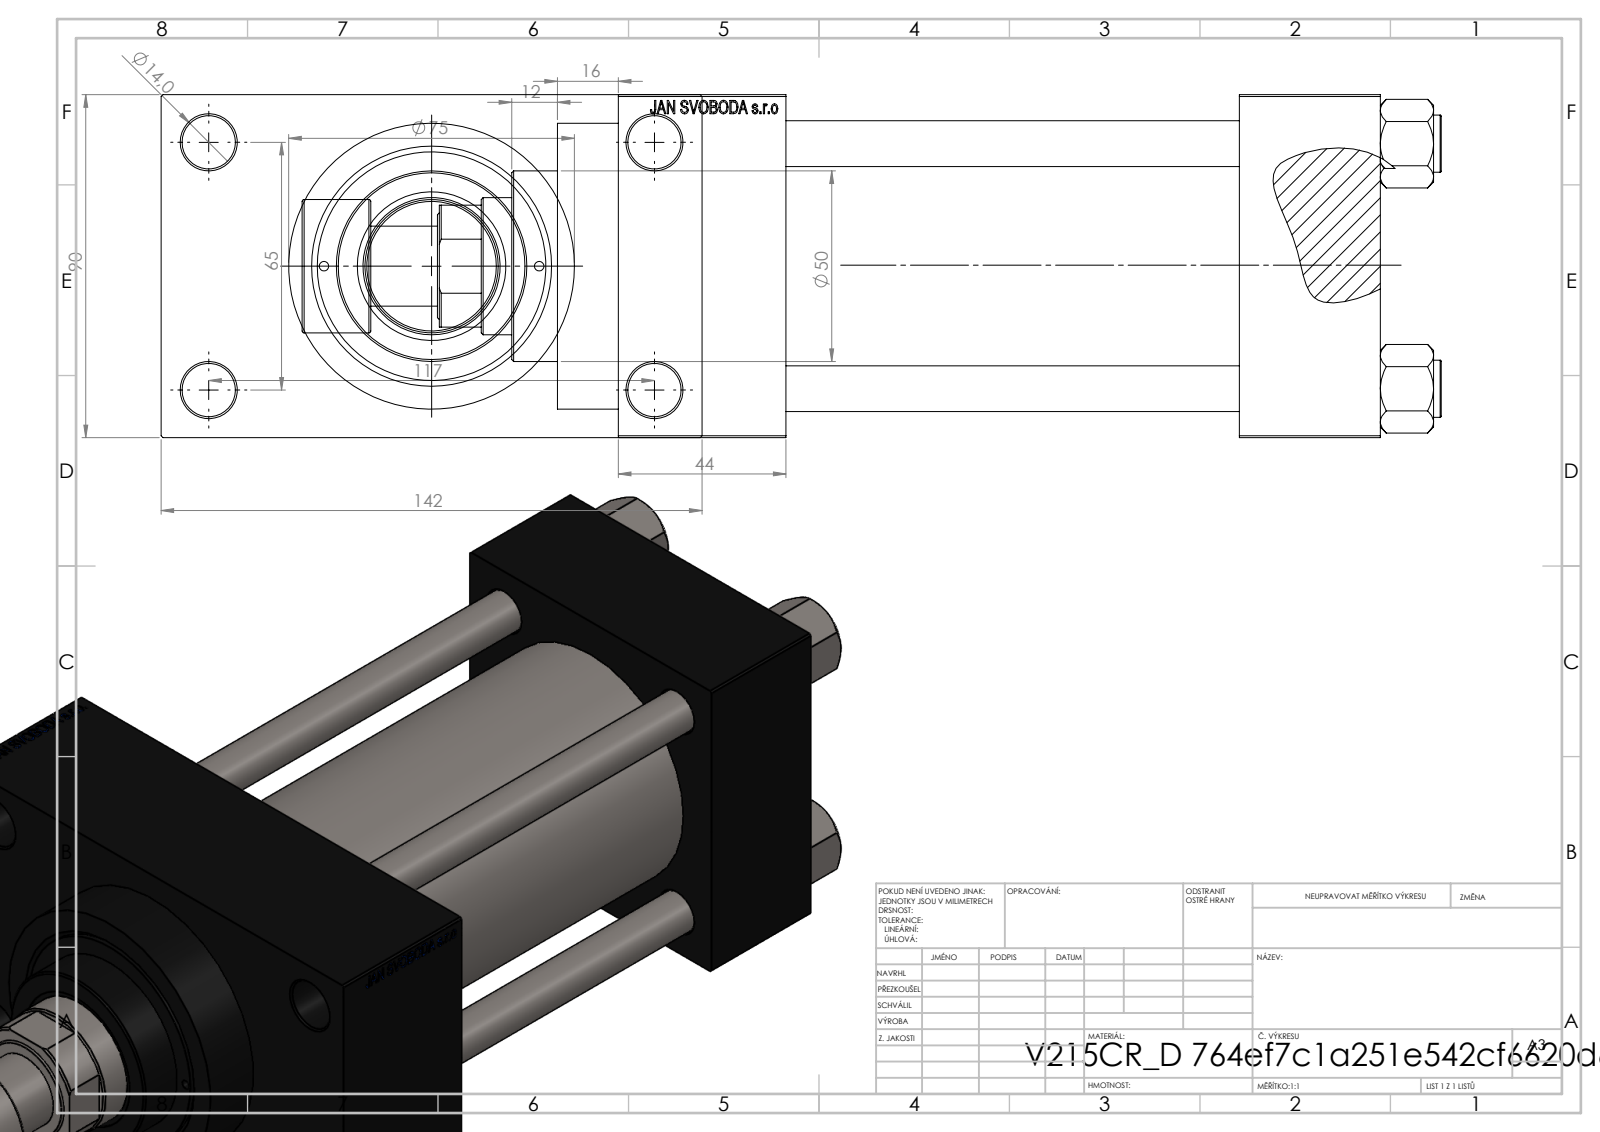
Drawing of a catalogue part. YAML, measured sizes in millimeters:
part_name: "V215CR_VCP_D; V215CR_ROD_END_F; V215CR_D_Body; NUT_M5_D (+2 more)"
step_written_by: "SolidWorks 2019 (CONFIG_CONTROL_DESIGN)"
units: millimeters
bodies: {solids: 12, faces: 1125, planar: 503, cylindrical: 96, other: 526}
overall_size: [299, 142, 90]
volume: 1261000
surface_area: 251982
round_holes:
  - {diameter: 12, count: 4}
  - {diameter: 14, count: 4}
  - {diameter: 2.5, count: 2}
  - {diameter: 7, count: 2}
  - {diameter: 20.96, count: 2}
  - {diameter: 30, count: 2}
  - {diameter: 25.5, count: 1}
  - {diameter: 36, count: 1}
  - {diameter: 39, count: 1}
  - {diameter: 50, count: 1}
  - {diameter: 60, count: 1}
  - {diameter: 63, count: 1}
round_bosses_or_shafts:
  - {diameter: 15, count: 4}
  - {diameter: 75, count: 1}
  - {diameter: 69, count: 1}
  - {diameter: 35, count: 1}
  - {diameter: 21, count: 1}
face_to_face_distances: [90, 119, 37, 156, 200, 163, 44, 26, 116, 142]
hole_center_spacings: [26.35, 32.39, 44.4, 45.47, 64.3, 66.92, 68.42, 69.81]
